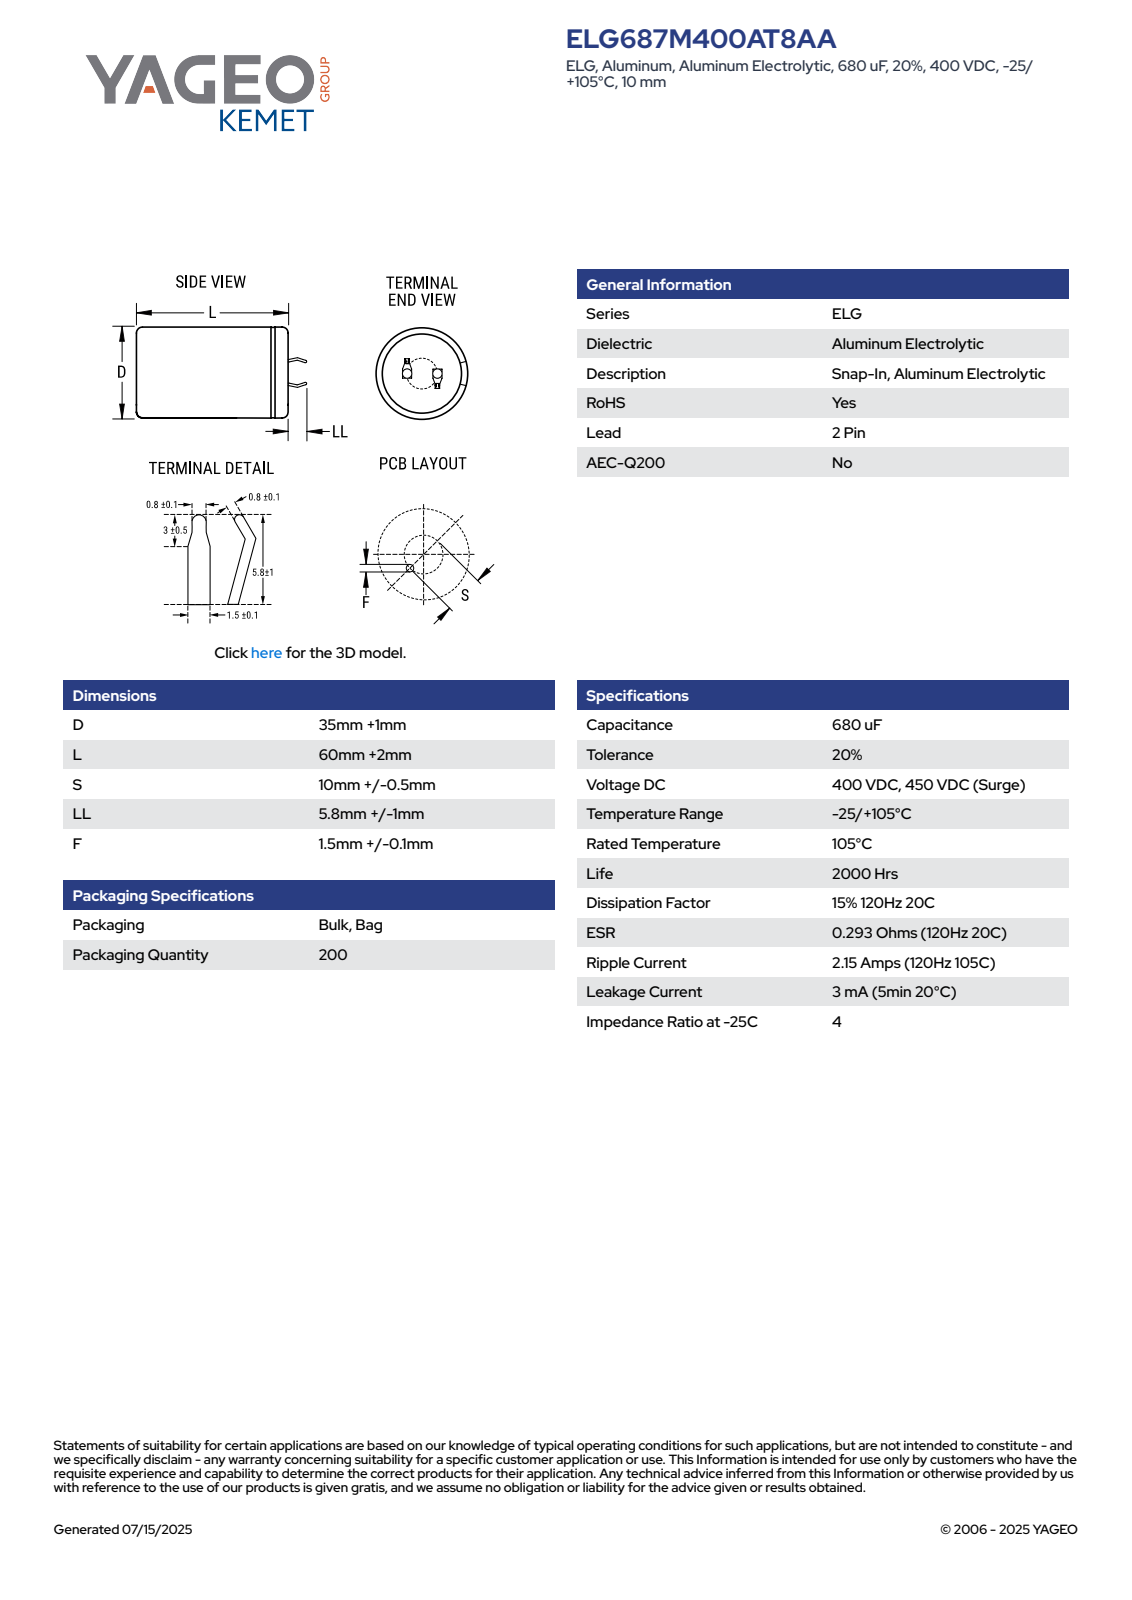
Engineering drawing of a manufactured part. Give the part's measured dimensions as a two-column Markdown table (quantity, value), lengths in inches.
| quantity | value |
| --- | --- |
| part name | CARS_K2P_35X60_D36L62S10LL6.8F1.6 |
| STEP written by | SolidWorks 2014 (AUTOMOTIVE_DESIGN) |
| units | inches |
| bodies | 1 solid, 100 faces (52 planar, 9 cylindrical, 39 other) |
| overall size | 2.708 × 1.417 × 1.417 |
| volume | 3.819 in³ |
| surface area | 14.02 in² |
| round holes (diameter × count) | 1.254 × 1 |
| round bosses / shafts (diameter × count) | 1.417 × 1 |
| partial cylindrical surfaces (radius × count) | 0.708 × 1 |
| main face-to-face distances | 2.441, 0.024, 2.46, 0.02, 0.279, 0.3, 0.03, 0.053, 0.302, 0.255 |
